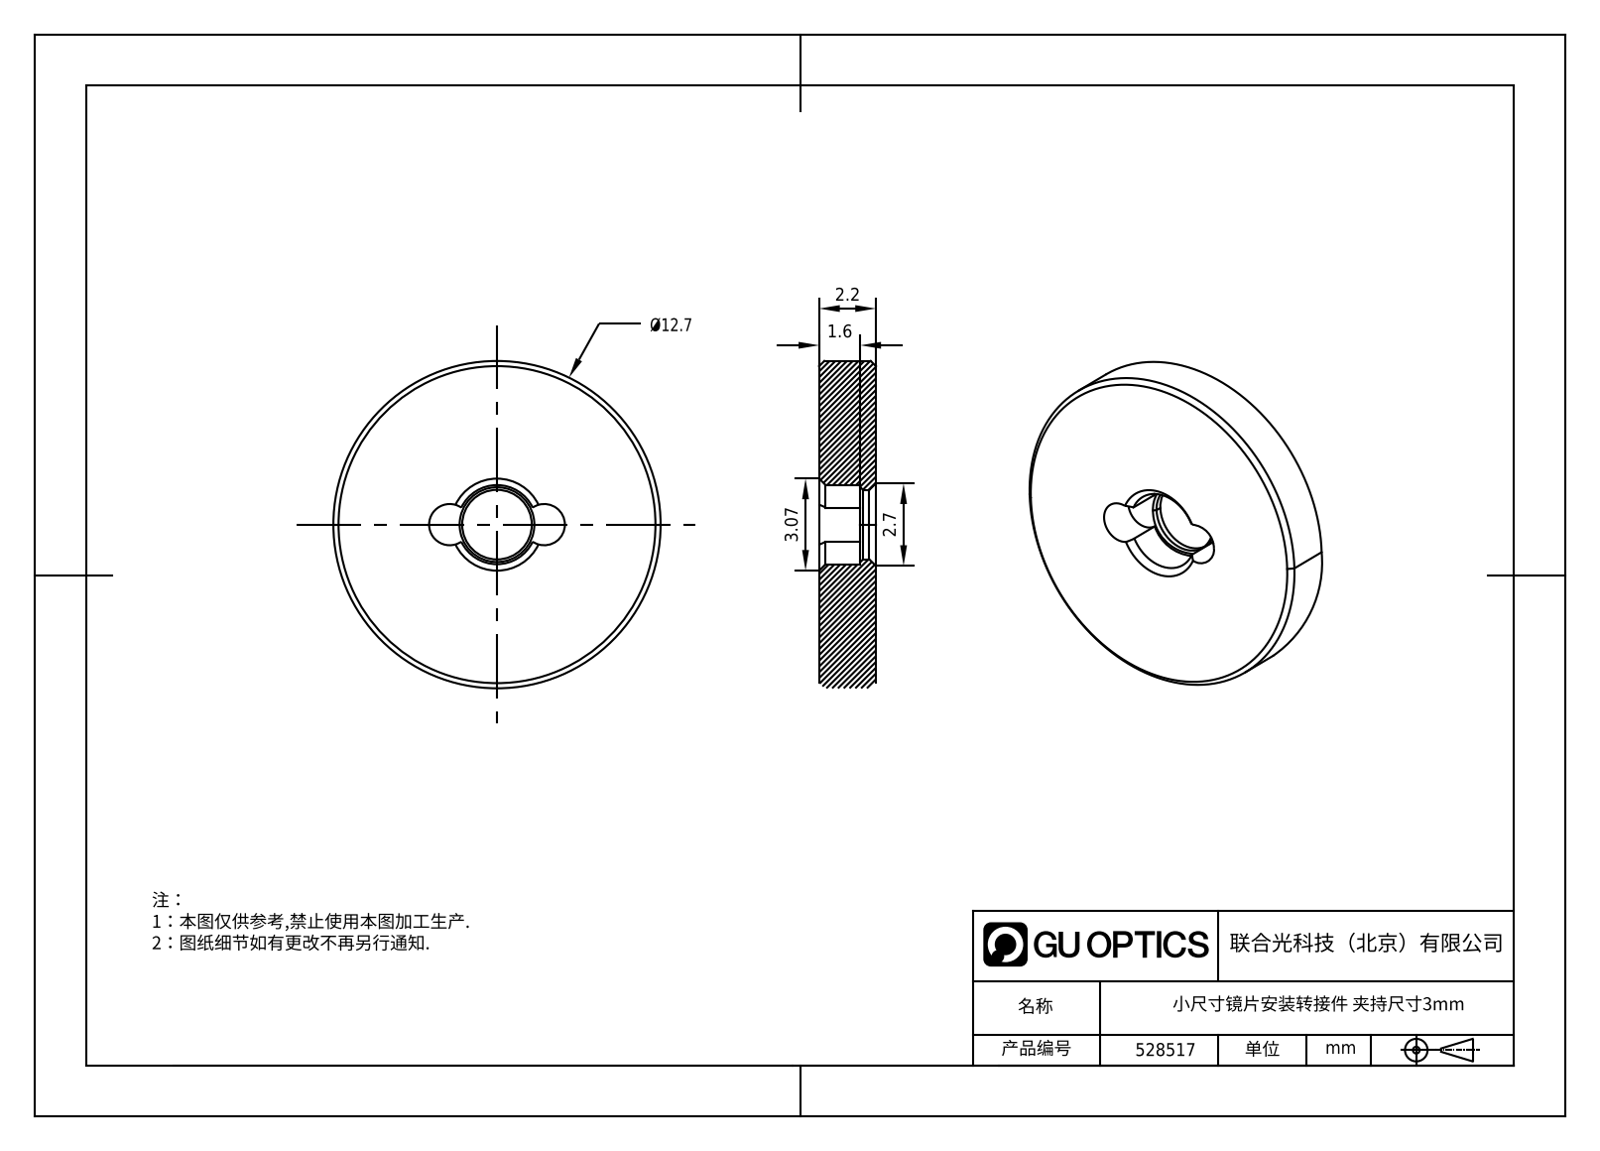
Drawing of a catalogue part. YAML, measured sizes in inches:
part_name: "1.6.4.3-ZSJ-05-3"
step_written_by: "SolidWorks 2021 (CONFIG_CONTROL_DESIGN)"
units: inches
bodies: {solids: 1, faces: 22, planar: 3, cylindrical: 9, other: 10}
overall_size: [0.5, 0.5, 0.087]
volume: 0.016
surface_area: 0.535
round_holes:
  - {diameter: 0.106, count: 1}
round_bosses_or_shafts:
  - {diameter: 0.5, count: 1}
partial_cylinders:
  - {radius: 0.031, count: 2}
  - {radius: 0.06, count: 1}
face_to_face_distances: [0.087, 0.024, 0.063]
